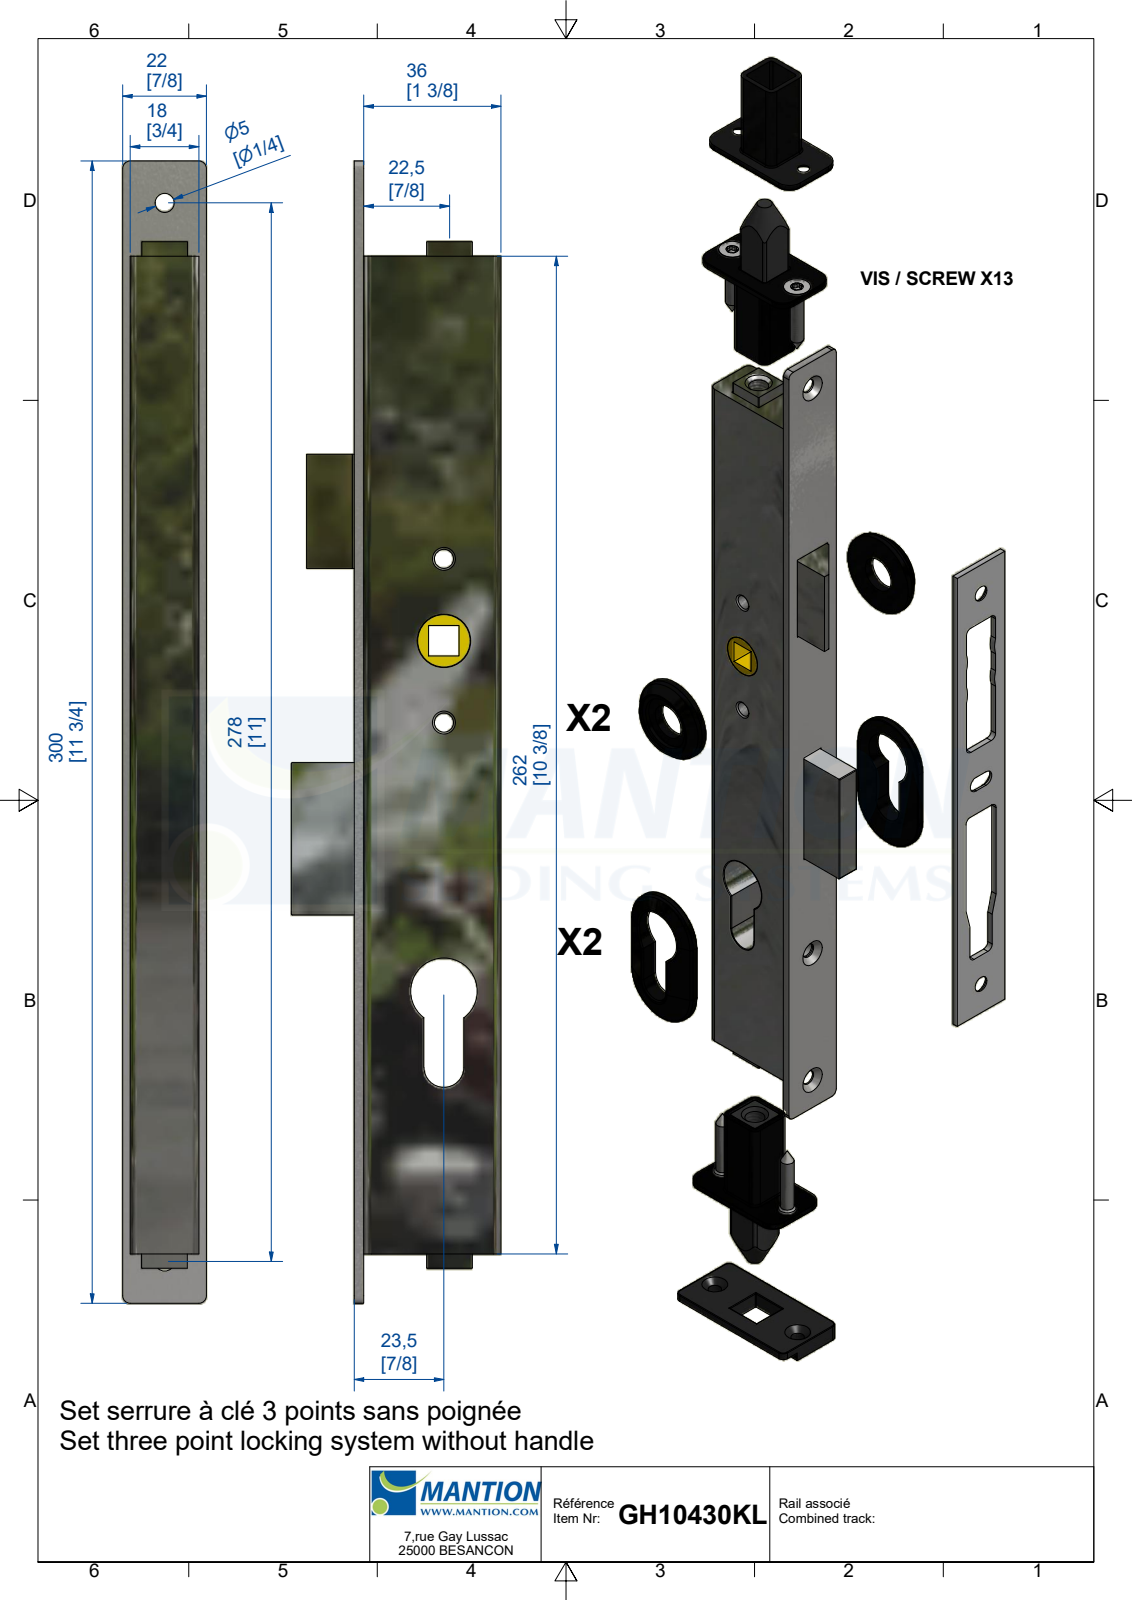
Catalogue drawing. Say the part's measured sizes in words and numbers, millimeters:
The part is named "GH10430KL; 23280; 23280-2; 23280-3 (+8 more)". Its 3-D file was written by "Autodesk Inventor 2019 (AUTOMOTIVE_DESIGN)". It is 20 solids with 542 faces: 188 planar, 240 cylindrical and 114 other. Overall it measures 571.04 by 130 by 101.72 millimeters. Its volume is 230 778 cubic millimeters and its surface area 95 742 square millimeters. Round holes: 5 of diameter 5, 2 of diameter 4.15, 2 of diameter 4.5, 2 of diameter 5.5, 2 of diameter 6.65, 1 of diameter 6.65, 1 of diameter 12, 1 of diameter 14, 1 of diameter 17.5, 1 of diameter 18, 1 of diameter 21. Round bosses or shafts: 2 of diameter 9, 2 of diameter 4.5, 1 of diameter 28, 1 of diameter 13.8. Partial cylindrical surfaces (rounded edges, fillets, slot ends): 44 of radius 0.25, 28 of radius 0.5, 24 of radius 0.39, 24 of radius 0.69, 20 of radius 2, 12 of radius 1, 8 of radius 0.75, 8 of radius 2.55. The main face-to-face distances are 18, 2, 2.5, 50, 52, 36, 11.85, 38.5, 52.5, 1.8. The hole center spacings are 15, 18.92, 19.48, 21.5, 3.92, 4.48, 20.5, 30.
